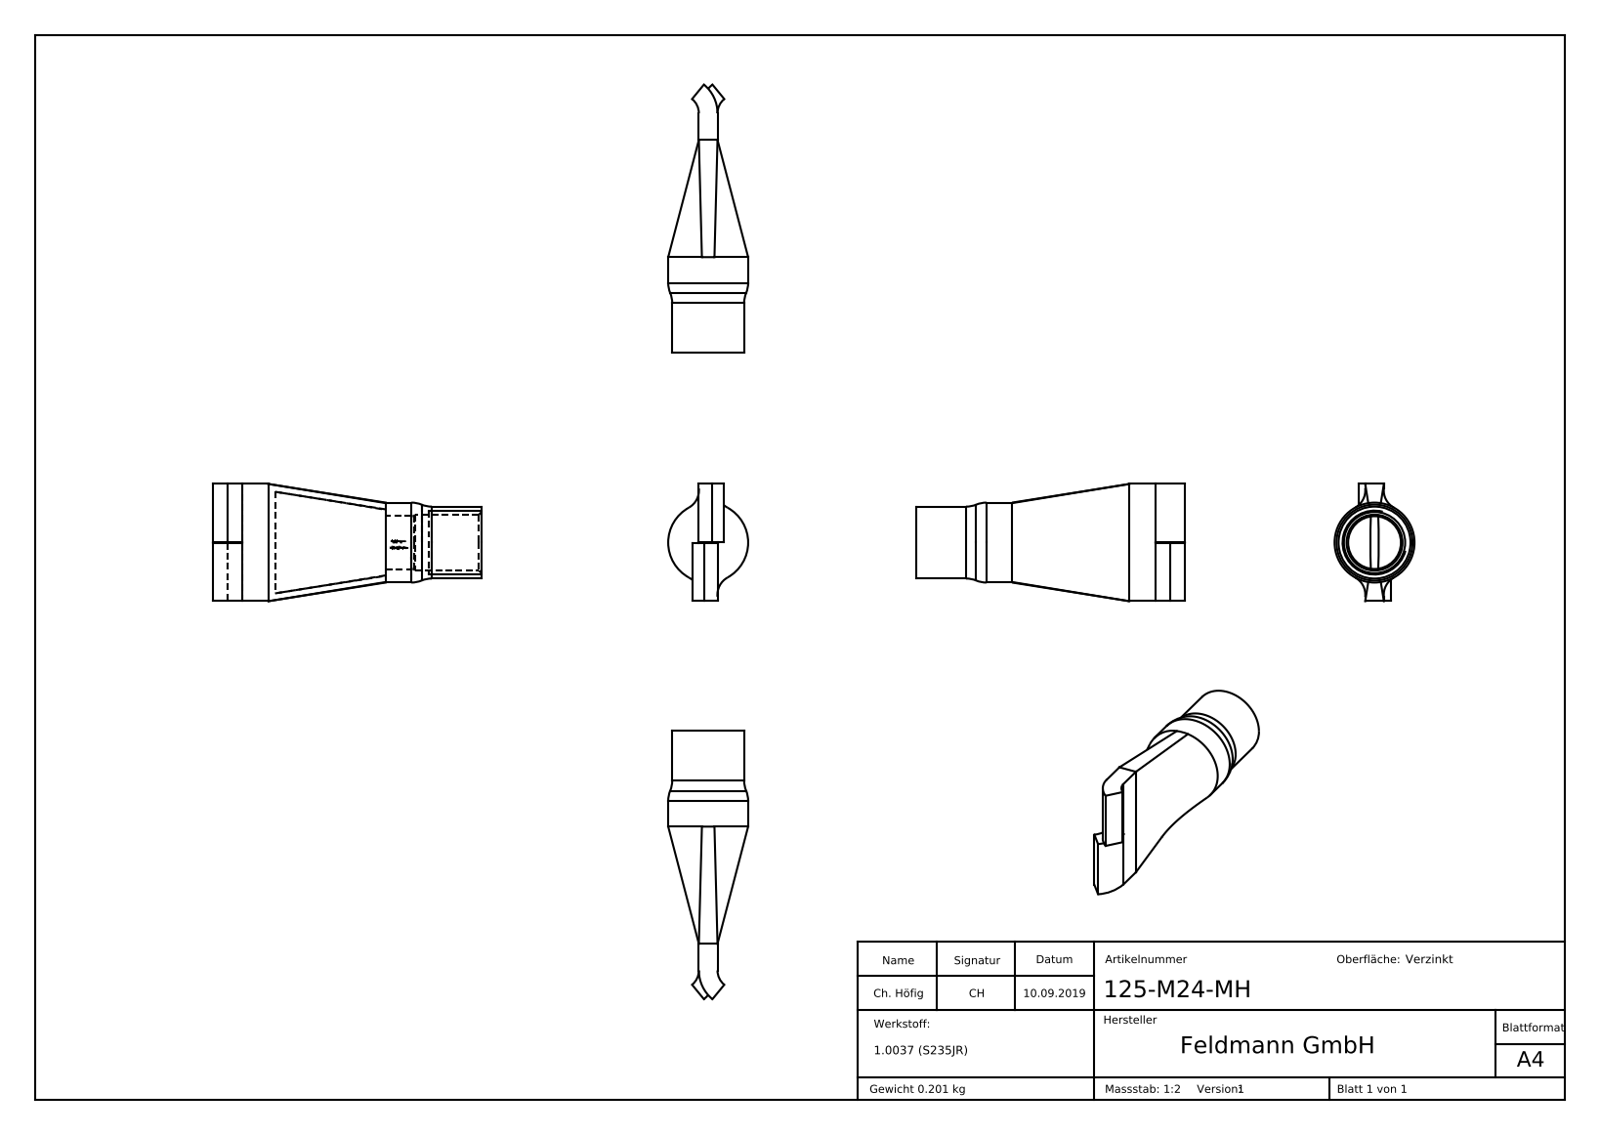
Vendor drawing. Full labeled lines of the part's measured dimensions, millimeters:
Part name (STEP PRODUCT): 125-M24-MH
STEP written by: SolidWorks 2015 (CONFIG_CONTROL_DESIGN)
Units: millimetres
Bodies: 1 solid, 278 faces (149 planar, 43 cylindrical, 86 other)
Overall size (bounding box): 100.77 × 44 × 30
Volume: 25 849 mm³ · Surface area: 15 786 mm²
Round holes (diameter × count): ⌀20 ×1, ⌀21 ×1
Round bosses / shafts (diameter × count): ⌀30 ×1, ⌀27 ×1
Partial cylindrical surfaces — rounded edges, fillets, slot ends (radius × count): R6.93 ×2, R13.93 ×2, R10.1 ×1
Main face-to-face distances: 7, 36, 44, 21.95, 22.05, 77.5, 41.5, 90, 54, 12.5
